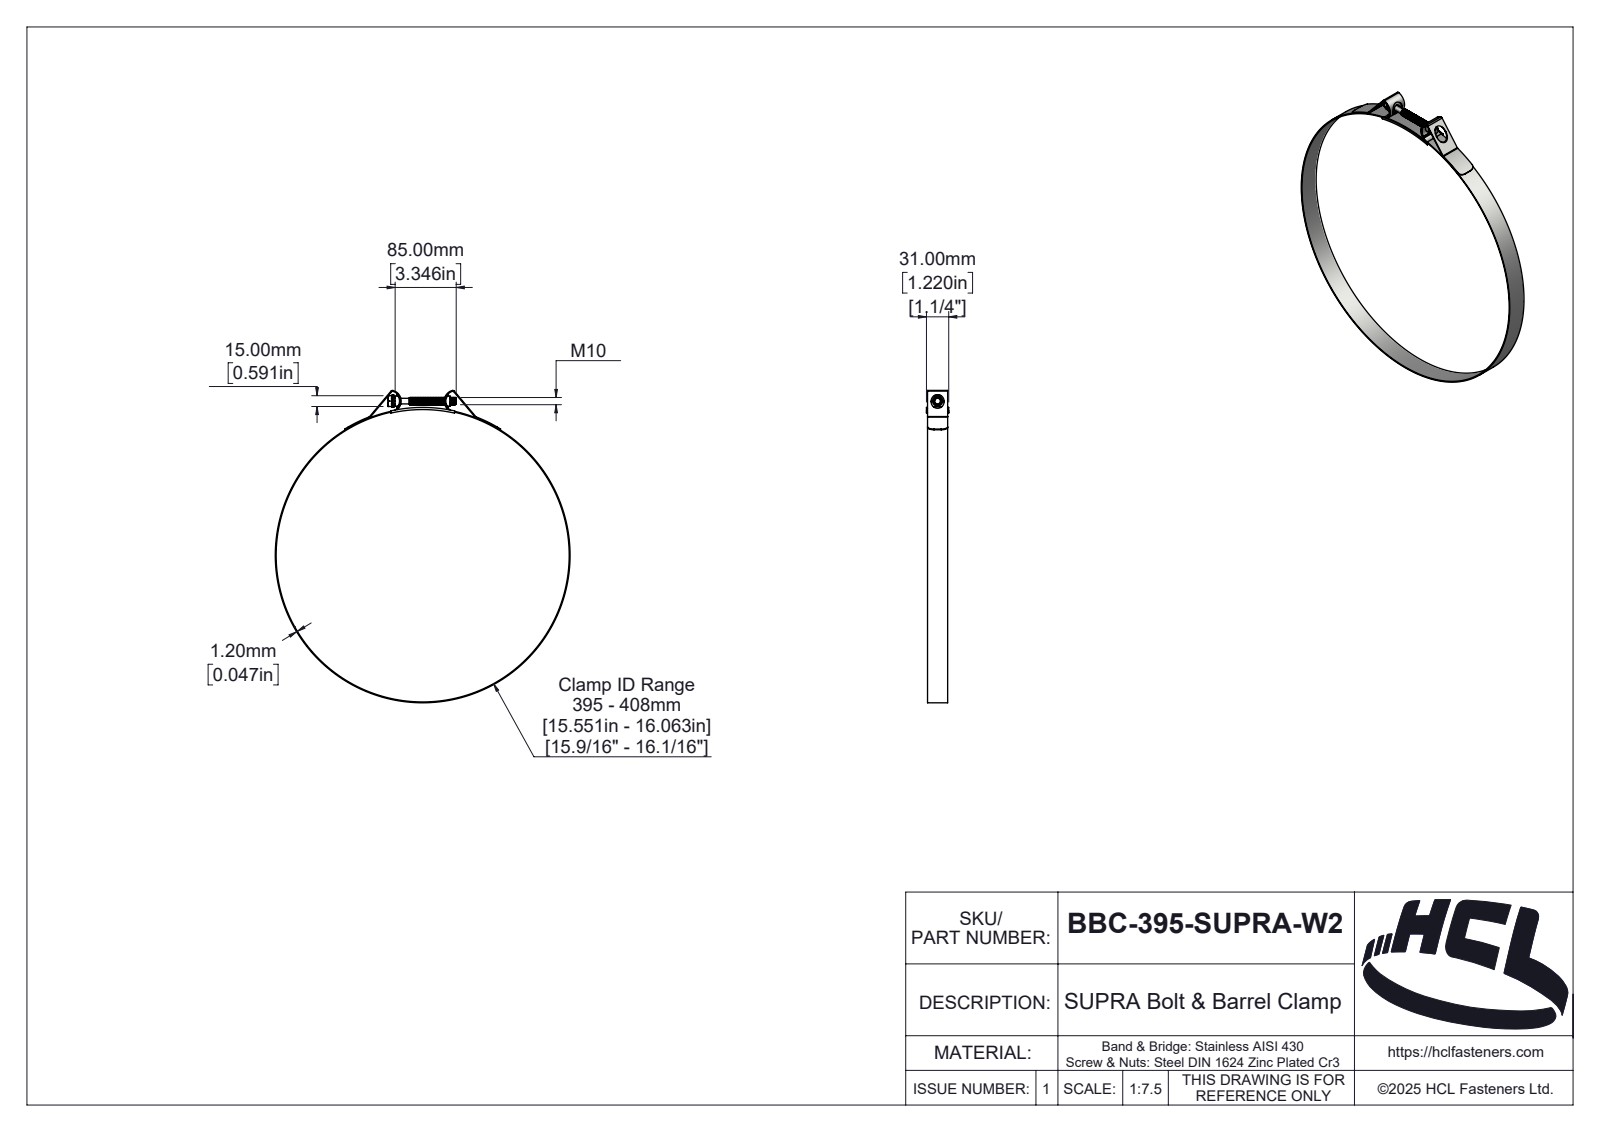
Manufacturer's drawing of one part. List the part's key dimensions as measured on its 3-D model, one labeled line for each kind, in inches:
Part name (STEP PRODUCT): BBC-395-SUPRA-W2
STEP written by: SolidWorks 2025 (AUTOMOTIVE_DESIGN)
Units: inches
Bodies: 5 solids, 376 faces (50 planar, 240 cylindrical, 86 other)
Overall size (bounding box): 17.113 × 16.157 × 1.22
Volume: 3.684 in³ · Surface area: 150.2 in²
Round holes (diameter × count): ⌀16.063 ×1
Round bosses / shafts (diameter × count): ⌀16.157 ×1, ⌀0.682 ×1, ⌀0.551 ×1, ⌀0.394 ×1, ⌀0.307 ×1
Partial cylindrical surfaces — rounded edges, fillets, slot ends (radius × count): R0.039 ×4, R0.051 ×2, R0.079 ×2, R0.098 ×2, R0.126 ×2, R0.354 ×2, R0.511 ×2, R0.551 ×2
Main face-to-face distances: 0.047, 1.102, 0.059, 1.161, 1.173, 1.114, 1.22, 1.126, 0.492, 3.313
